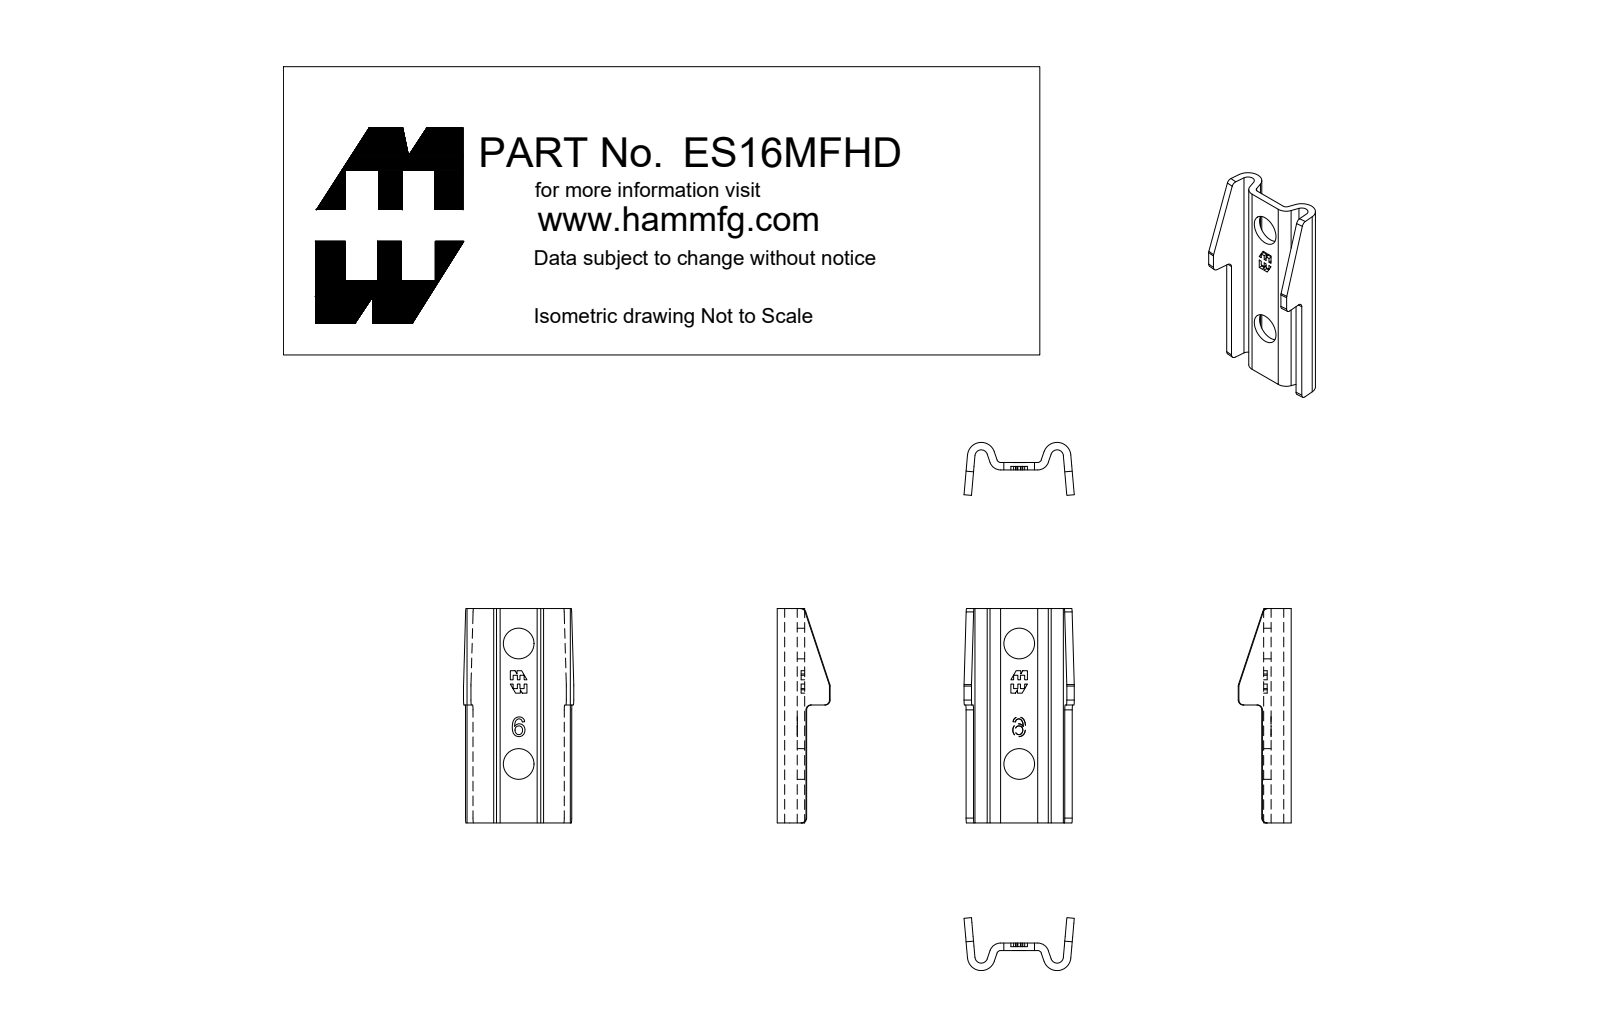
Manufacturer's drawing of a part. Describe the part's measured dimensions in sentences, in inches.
The part is named "ES16MFHD". Its 3-D file was written by "SolidWorks 2018 (AUTOMOTIVE_DESIGN)". It is 1 solid with 81 faces: 55 planar, 22 cylindrical and 4 other. Overall it measures 2.726 by 1.402 by 0.673 inches. Its volume is 0.543 cubic inches and its surface area 12.73 square inches. Round holes: 2 of diameter 0.39. Partial cylindrical surfaces (rounded edges, fillets, slot ends): 9 of radius 0.062, 2 of radius 0.048, 2 of radius 0.08, 2 of radius 0.143, 2 of radius 0.175, 1 of radius 0.063. The main face-to-face distances are 0.095, 0.095, 2.726, 0.299, 1.5, 1.226, 0.05, 0.045, 0.049, 0.094. The hole center spacings are 1.531.
